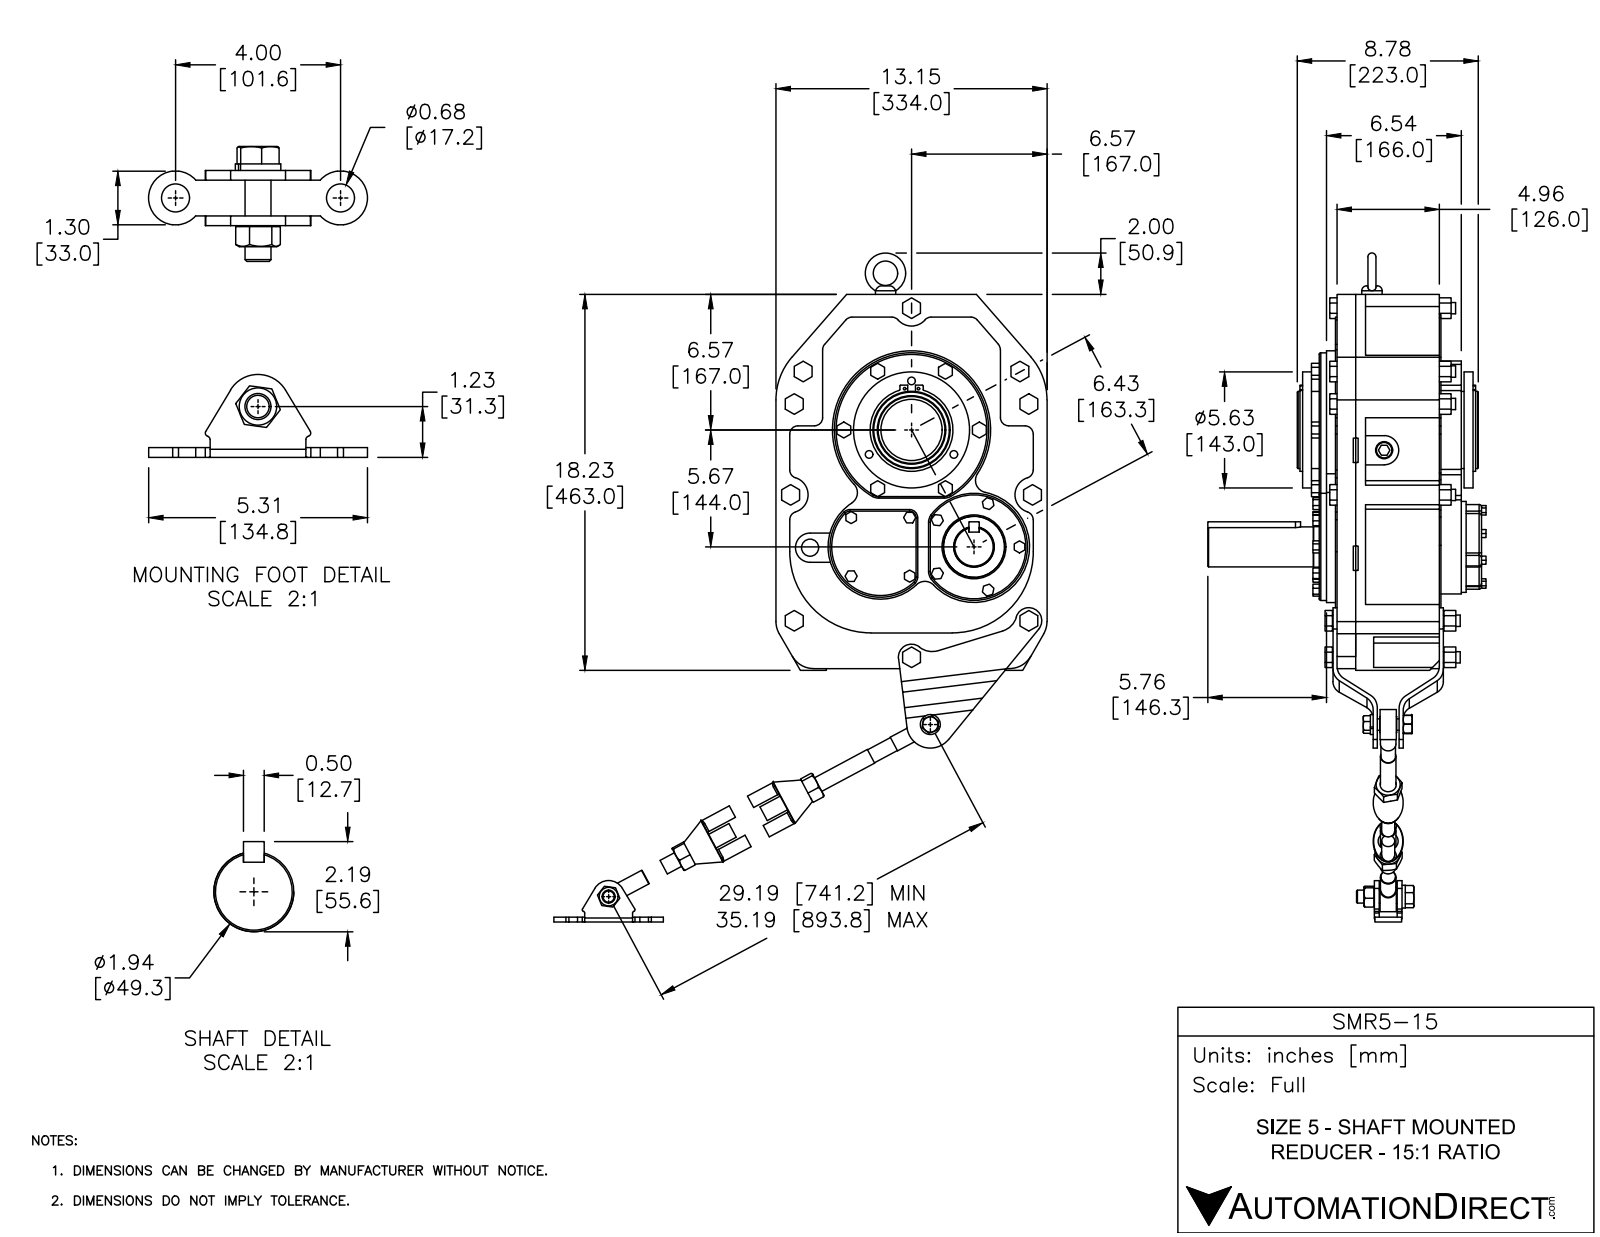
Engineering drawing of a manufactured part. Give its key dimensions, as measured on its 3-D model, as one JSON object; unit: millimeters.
{"part_name": "SMR5-TA_5; SMR5-TA_4; SMR5-TA_3; SMR5-TA_2 (+4 more)", "step_written_by": "SolidWorks 2016 (AUTOMOTIVE_DESIGN)", "units": "millimeters", "bodies": {"solids": 74, "faces": 1347, "planar": 740, "cylindrical": 451, "other": 156}, "overall_size": [875.3, 703.8, 342.7], "volume_mm3": 19660000, "surface_area_mm2": 1595000, "round_holes": [[15, 12], [13.5, 8], [21, 5], [9.3, 3], [3, 2], [17.2, 2], [17.5, 2], [20, 2], [14, 1], [14.2, 1], [14.5, 1], [16, 1]], "round_bosses_or_shafts": [[14, 10], [19.1, 4], [37, 2], [18.1, 2], [16, 2], [190, 1], [143, 1], [132, 1]], "partial_cylinders_radius": [[10, 31], [15, 19], [3, 12], [2, 8], [22, 5], [1, 4], [7, 4], [18, 4]], "face_to_face_distances": [25, 2, 130, 128, 36, 13, 11, 22, 153, 23], "hole_center_spacings": [93, 131.5, 60.3, 75.8, 104.4, 267, 12.8, 38.1]}
